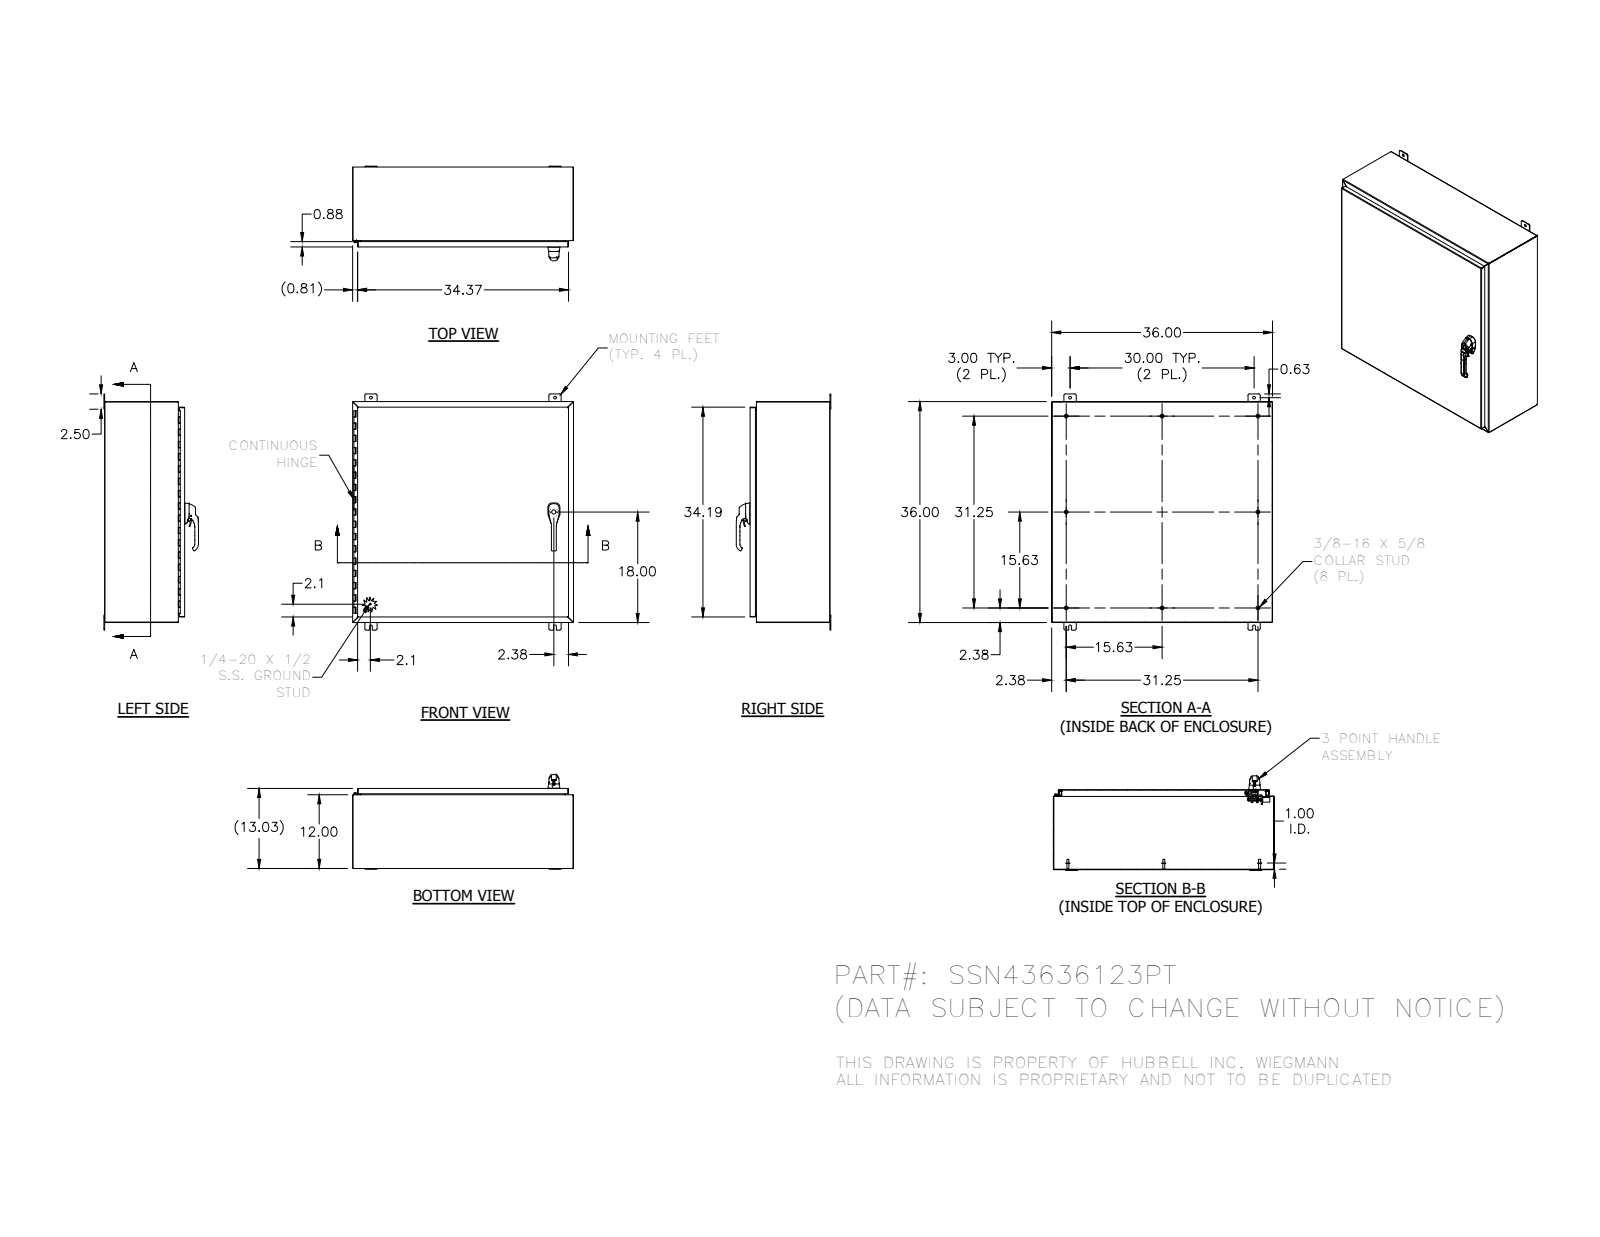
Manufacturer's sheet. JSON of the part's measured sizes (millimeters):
{"part_name": "1091-75; 32874-36P; PLASTIC-ROLLER-CAM_AF0_ASM; 32874-36T (+8 more)", "step_written_by": "SolidWorks 2014 (AUTOMOTIVE_DESIGN)", "units": "millimeters", "bodies": {"solids": 62, "faces": 3213, "planar": 1120, "cylindrical": 1308, "other": 785}, "overall_size": [977.9, 914.4, 391.4], "volume_mm3": 6180000, "surface_area_mm2": 6386000, "round_holes": [[6.7, 8], [4.7, 4], [11.1, 4], [5.4, 3], [7.1, 3], [6.1, 2], [6.4, 2], [6.4, 2], [8, 2], [10.2, 2], [10.2, 2], [10.5, 2]], "round_bosses_or_shafts": [[15.9, 8], [8.4, 8], [6, 3], [25.4, 2], [14.3, 2], [13.5, 2], [13.5, 2], [12.7, 2]], "partial_cylinders_radius": [[0.5, 172], [0.3, 113], [3.2, 26], [0.8, 22], [0.5, 21], [6.4, 20], [2.7, 18], [1.3, 15]], "face_to_face_distances": [1.9, 329.2, 912.5, 327.3, 331, 910.6, 914.4, 302.9, 26.2, 304.8], "hole_center_spacings": [9.7, 12.5, 19.3, 22.5, 671.3, 5.9, 6.6, 9.7]}
